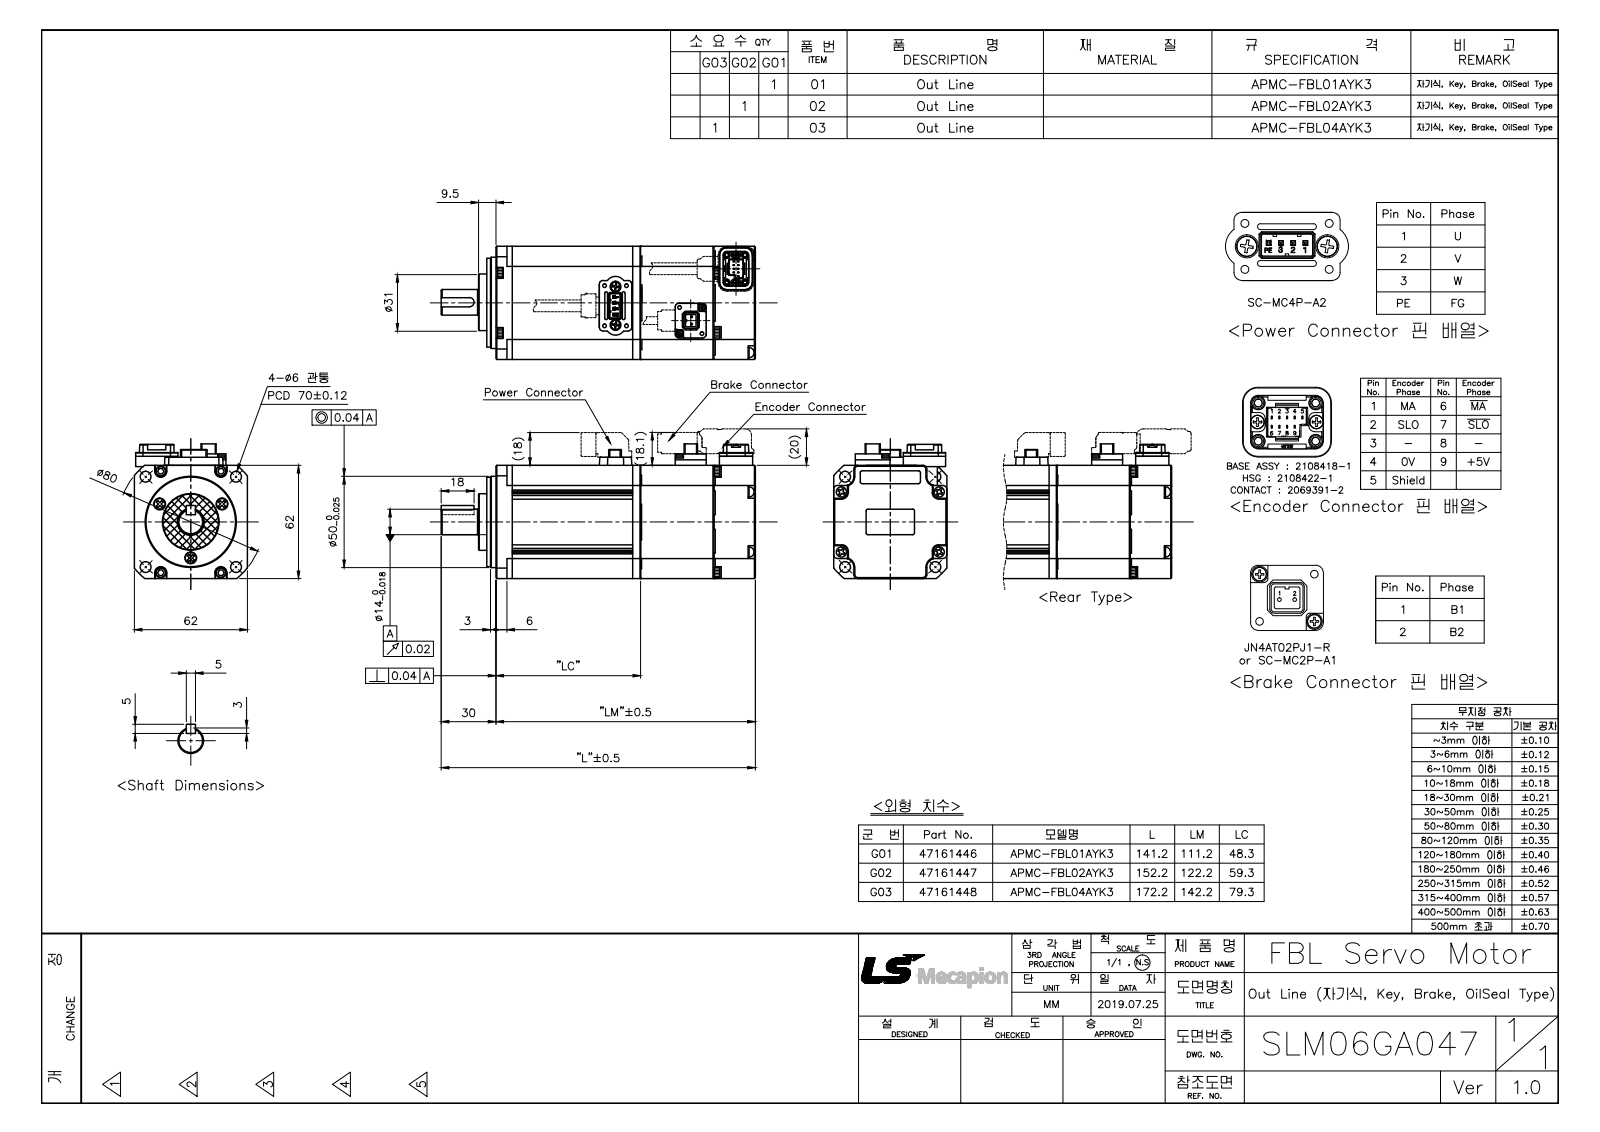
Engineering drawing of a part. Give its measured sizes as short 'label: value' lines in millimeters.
name: SLM06GA043G01_Out Line(APMC-FBL01AYK2)
written by: SolidWorks 2011 (AUTOMOTIVE_DESIGN)
unit: mm
bodies: 51 solids, 2104 faces (1309 planar, 582 cylindrical, 213 other)
size: 141.2 × 73.8 × 62
volume: 390 862 mm³; area: 95 732 mm²
holes: 10× ⌀2.1, 10× ⌀3, 8× ⌀3.5, 6× ⌀1.6, 6× ⌀6, 4× ⌀2, 4× ⌀3.1, 2× ⌀1, 1× ⌀3.3, 1× ⌀3.4, 1× ⌀13, 1× ⌀15.3
bosses: 6× ⌀5.4, 4× ⌀5.6, 4× ⌀5.5, 2× ⌀4.2, 2× ⌀3.6, 2× ⌀3.5, 2× ⌀2.2, 2× ⌀0.9
rounds: 20× R0.2, 20× R0.3, 12× R1, 12× R2, 12× R3, 9× R0.15, 7× R0.45, 6× R0.11
face distances: 62, 4.3, 0.7, 35, 0.5, 39.3, 44.5, 40.2, 79.5, 40.9
hole spacings: 5, 6.02, 8.5, 8.8, 9.43, 15.29, 16, 22.32
